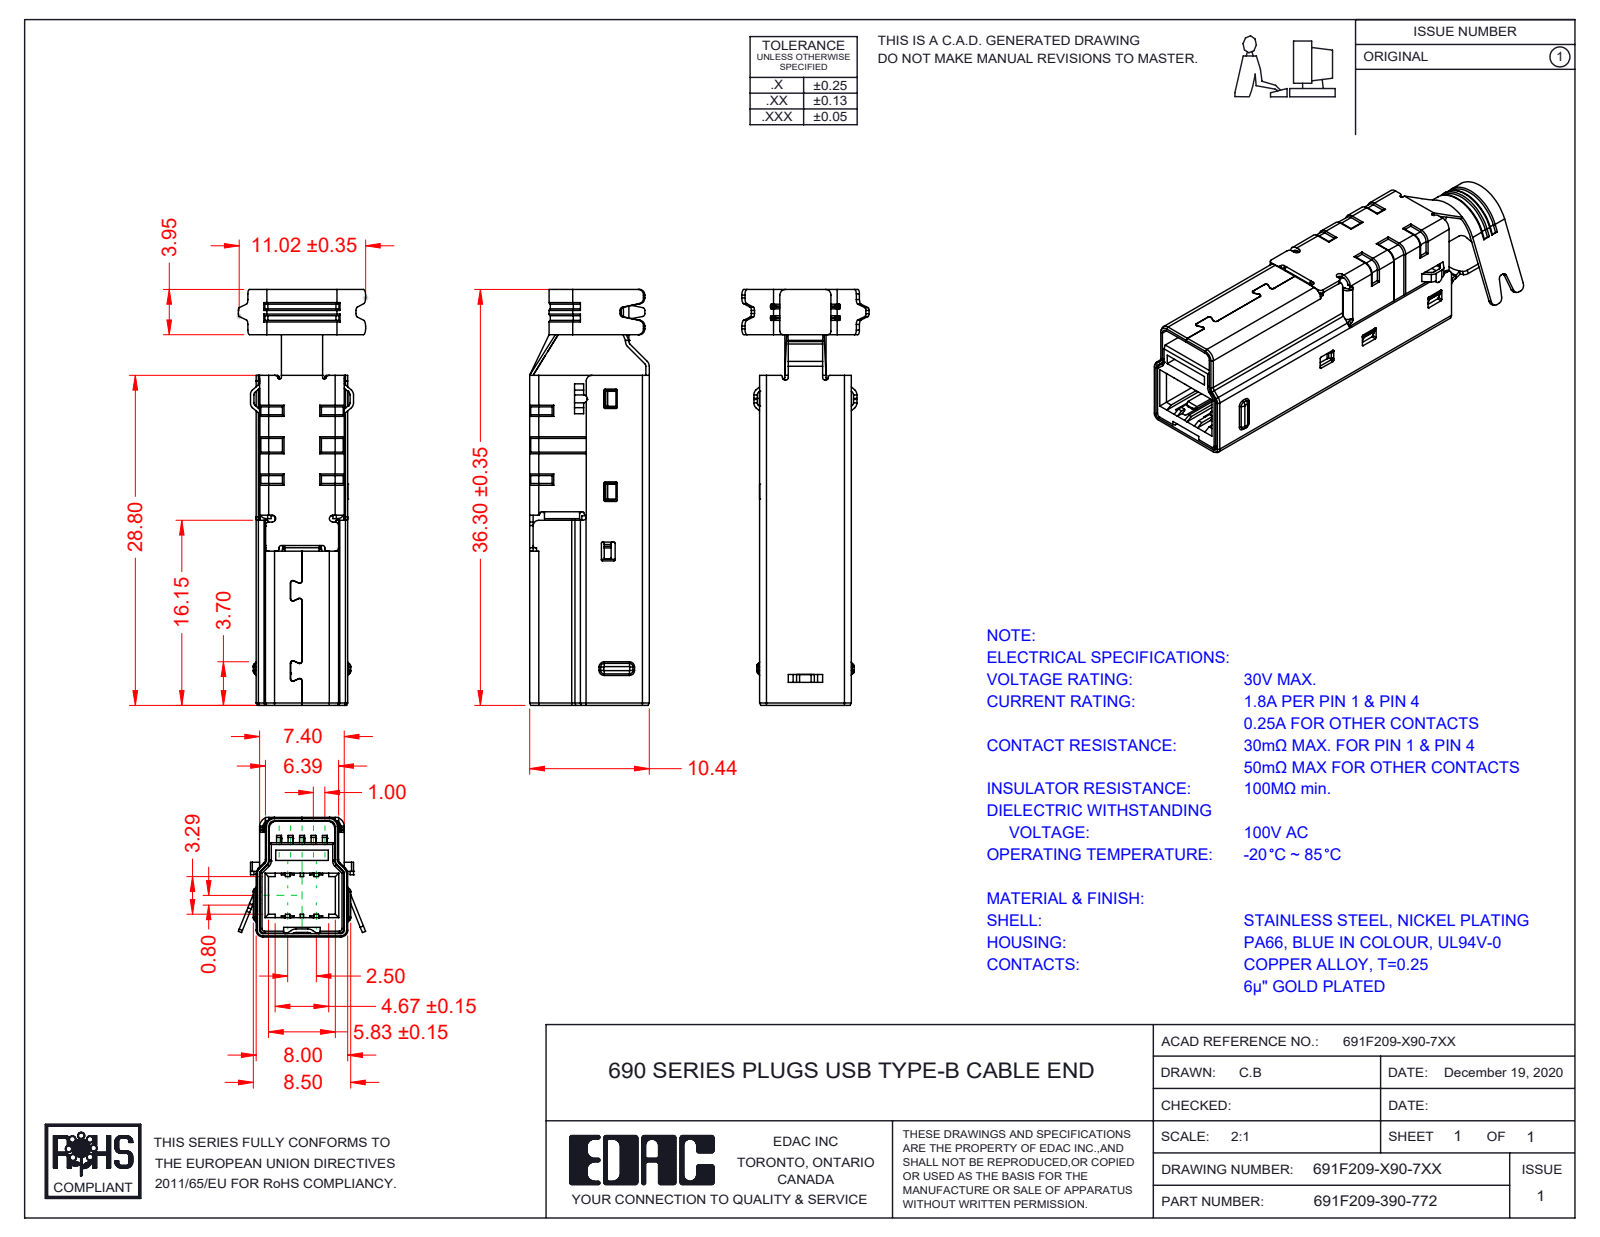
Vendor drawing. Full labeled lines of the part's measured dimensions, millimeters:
Part name (STEP PRODUCT): Shell 2 691F209-X90-7XX; Insulator 691F209-X90-7XX_Blue; Shell 1 691F209-X90-7XX; 691F209-190-712 (+1 more)
STEP written by: SolidWorks 2020 (AUTOMOTIVE_DESIGN)
Units: millimetres
Bodies: 12 solids, 1476 faces (812 planar, 525 cylindrical, 139 other)
Overall size (bounding box): 36.3 × 11.11 × 10.44
Volume: 931 mm³ · Surface area: 3 750 mm²
Partial cylindrical surfaces — rounded edges, fillets, slot ends (radius × count): R0.15 ×130, R0.1 ×56, R0.3 ×44, R0.2 ×29, R0.5 ×22, R0.6 ×12, R0.4 ×10, R0.2 ×8
Main face-to-face distances: 7.4, 10.14, 7.7, 0.6, 7.1, 9.84, 0.81, 10.44, 8, 0.34
